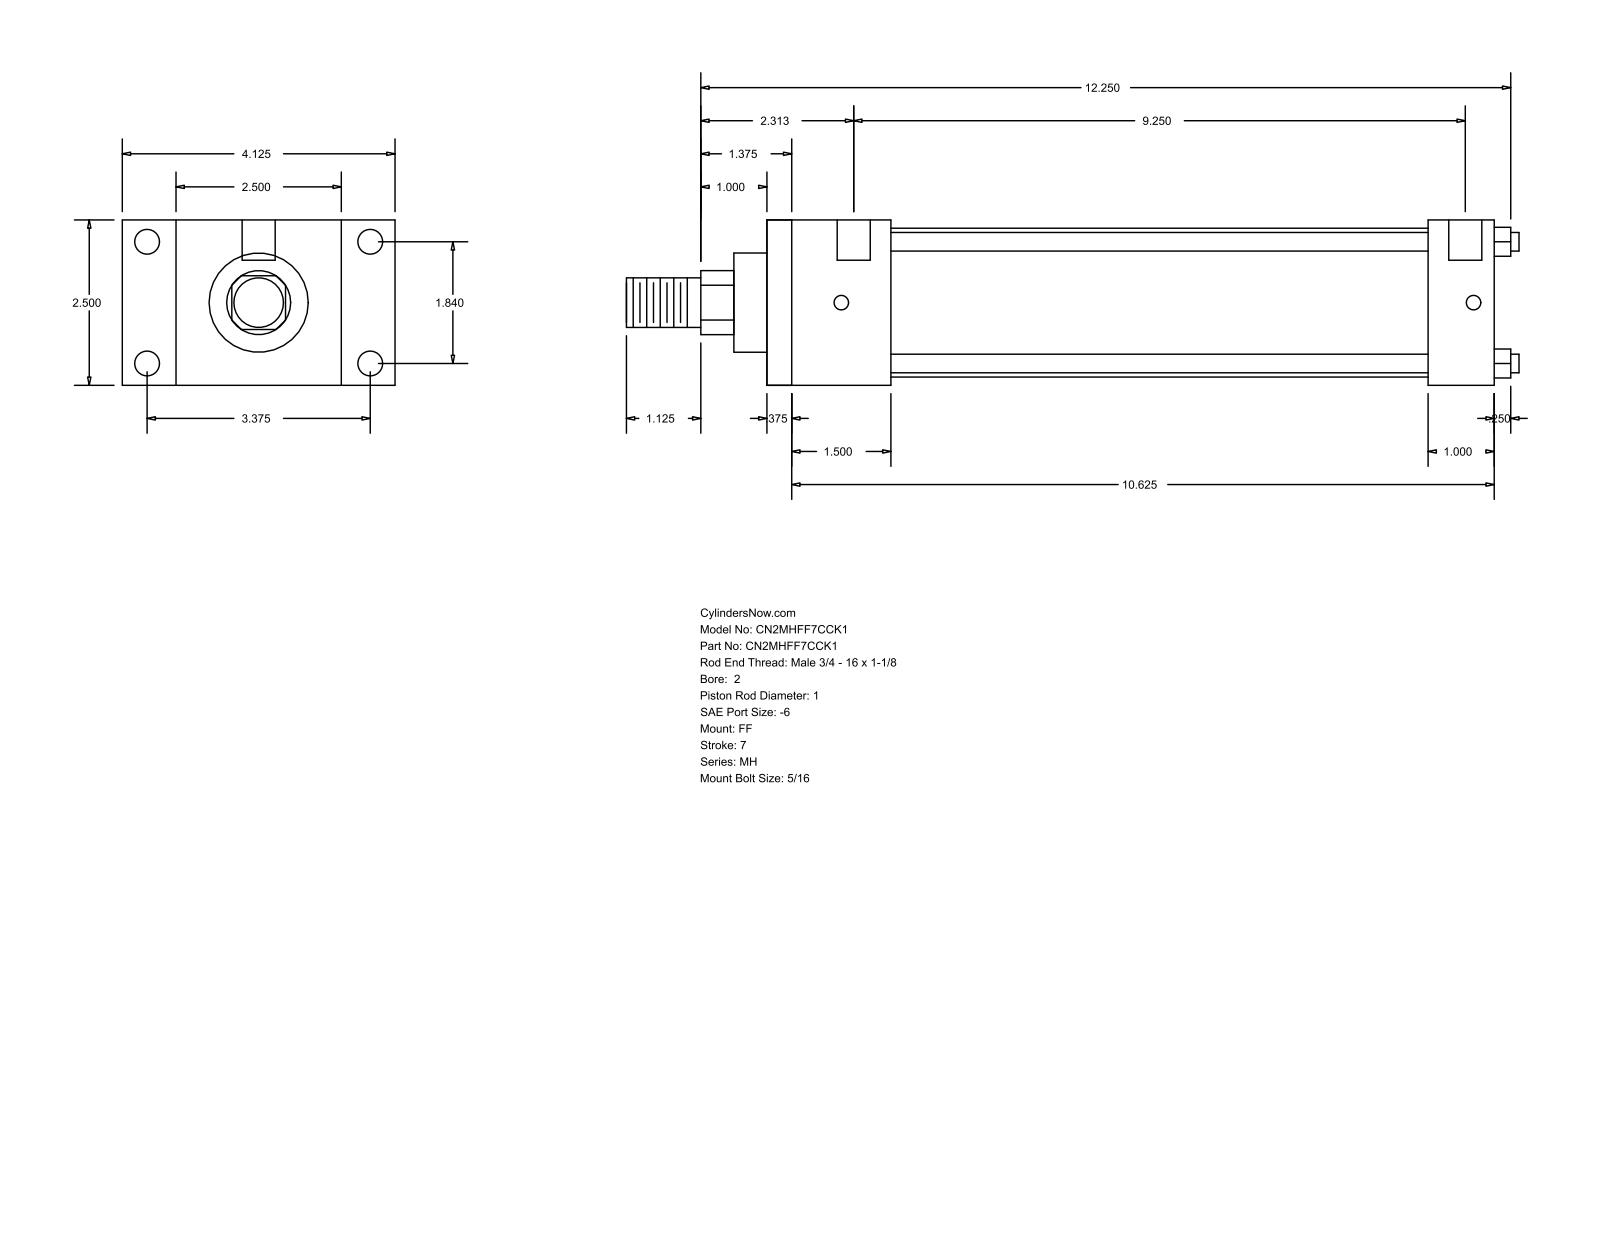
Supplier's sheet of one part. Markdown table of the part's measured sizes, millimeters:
| quantity | value |
| --- | --- |
| part name | MH_FF__0200_1 |
| STEP written by | GSSL Pune (CONFIG_CONTROL_DESIGN) |
| units | millimeters |
| bodies | 0 solids, 92 faces (64 planar, 28 cylindrical, 0 other) |
| overall size | 342.9 × 104.78 × 63.5 |
| round holes (diameter × count) | 5.56 × 4, 9.53 × 4, 12.7 × 2 |
| round bosses / shafts (diameter × count) | 7.14 × 4, 57.15 × 1, 38.1 × 1, 25.4 × 1, 19.05 × 1 |
| partial cylindrical surfaces (radius × count) | 12.29 × 1 |
| main face-to-face distances | 63.5, 279.4, 9.52, 269.88, 20.64, 25.4, 47.63, 254, 38.11, 244.48 |
| hole center spacings | 46.74, 85.72, 97.63, 242.88, 3.17, 4.76, 234.95, 238.12 |
